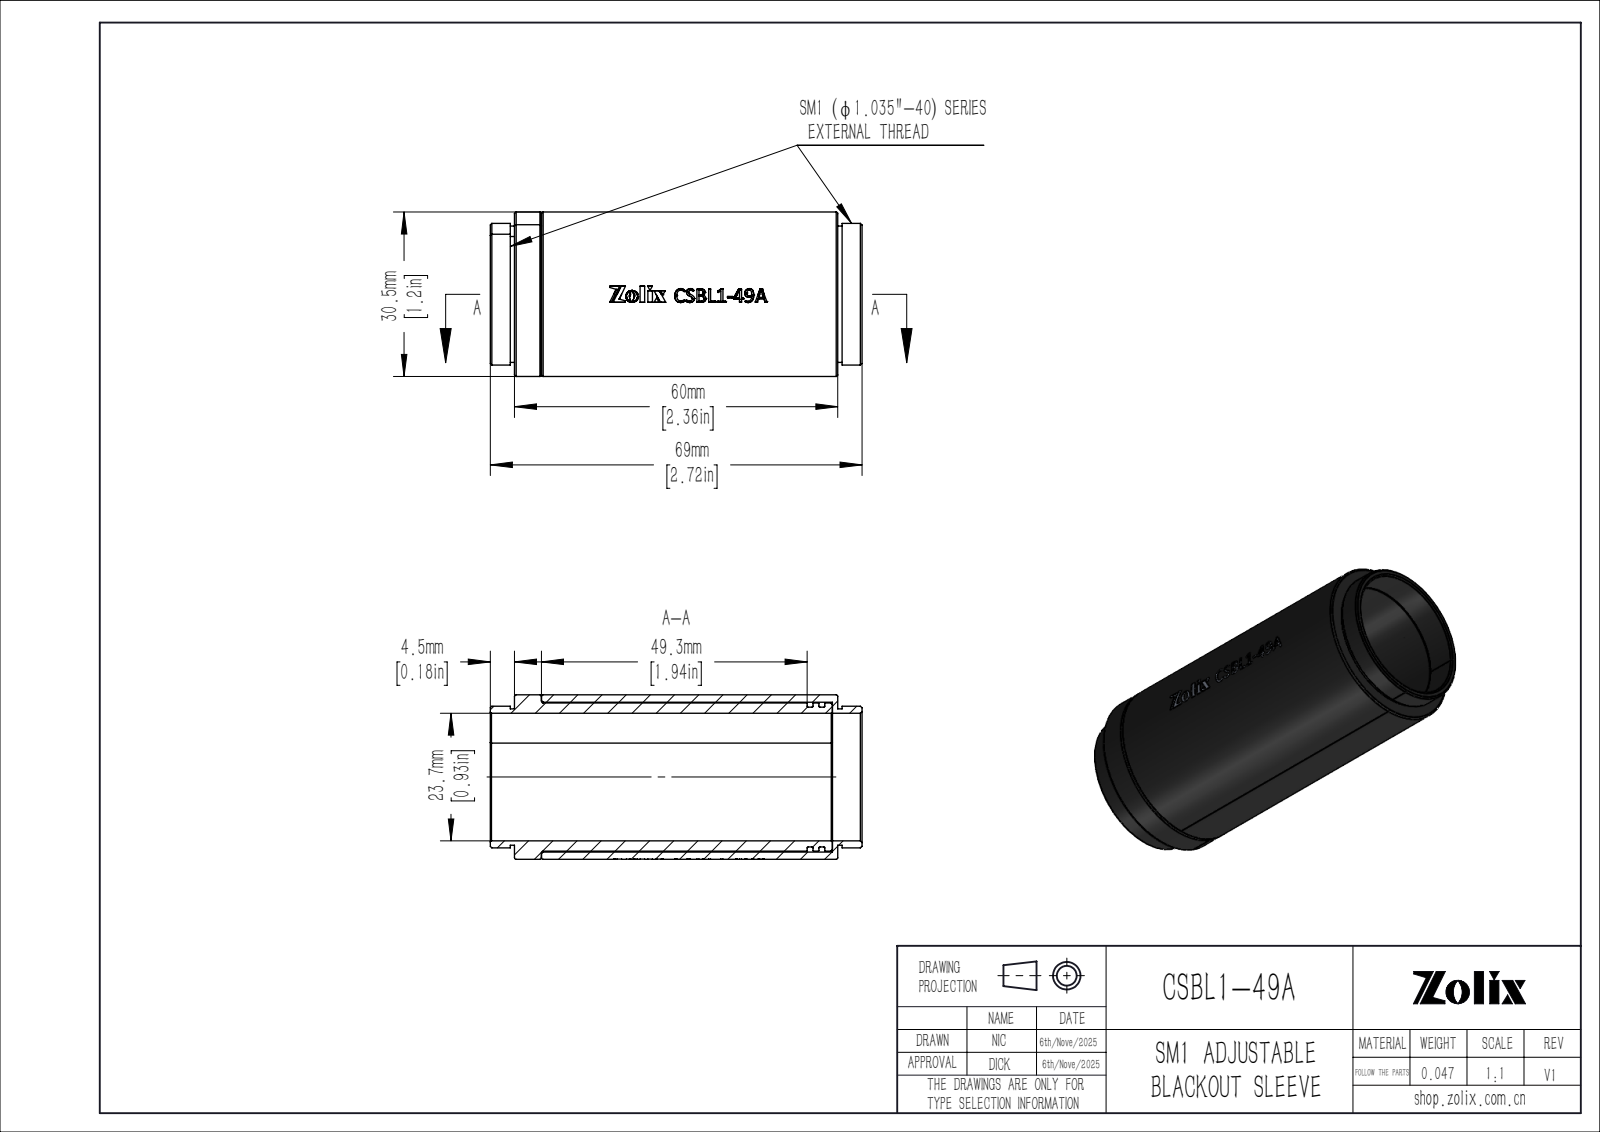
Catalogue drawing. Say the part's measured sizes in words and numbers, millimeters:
The part is named "CSBL1-49A". Its 3-D file was written by "SolidWorks 2020 (CONFIG_CONTROL_DESIGN)". It is 2 solids with 387 faces: 67 planar, 52 cylindrical and 268 other. Overall it measures 69 by 30.5 by 30.5 millimeters. Its volume is 17 370 cubic millimeters and its surface area 22 395 square millimeters. Round holes: 1 of diameter 23.7, 1 of diameter 27.8. Round bosses or shafts: 1 of diameter 30.5, 1 of diameter 27.5, 1 of diameter 26.3, 1 of diameter 25.9, 1 of diameter 25.3. Partial cylindrical surfaces (rounded edges, fillets, slot ends): 1 of radius 15.23. The main face-to-face distances are 59, 1, 60, 55, 54, 5, 1.1, 4.5, 64.5, 2.2.
